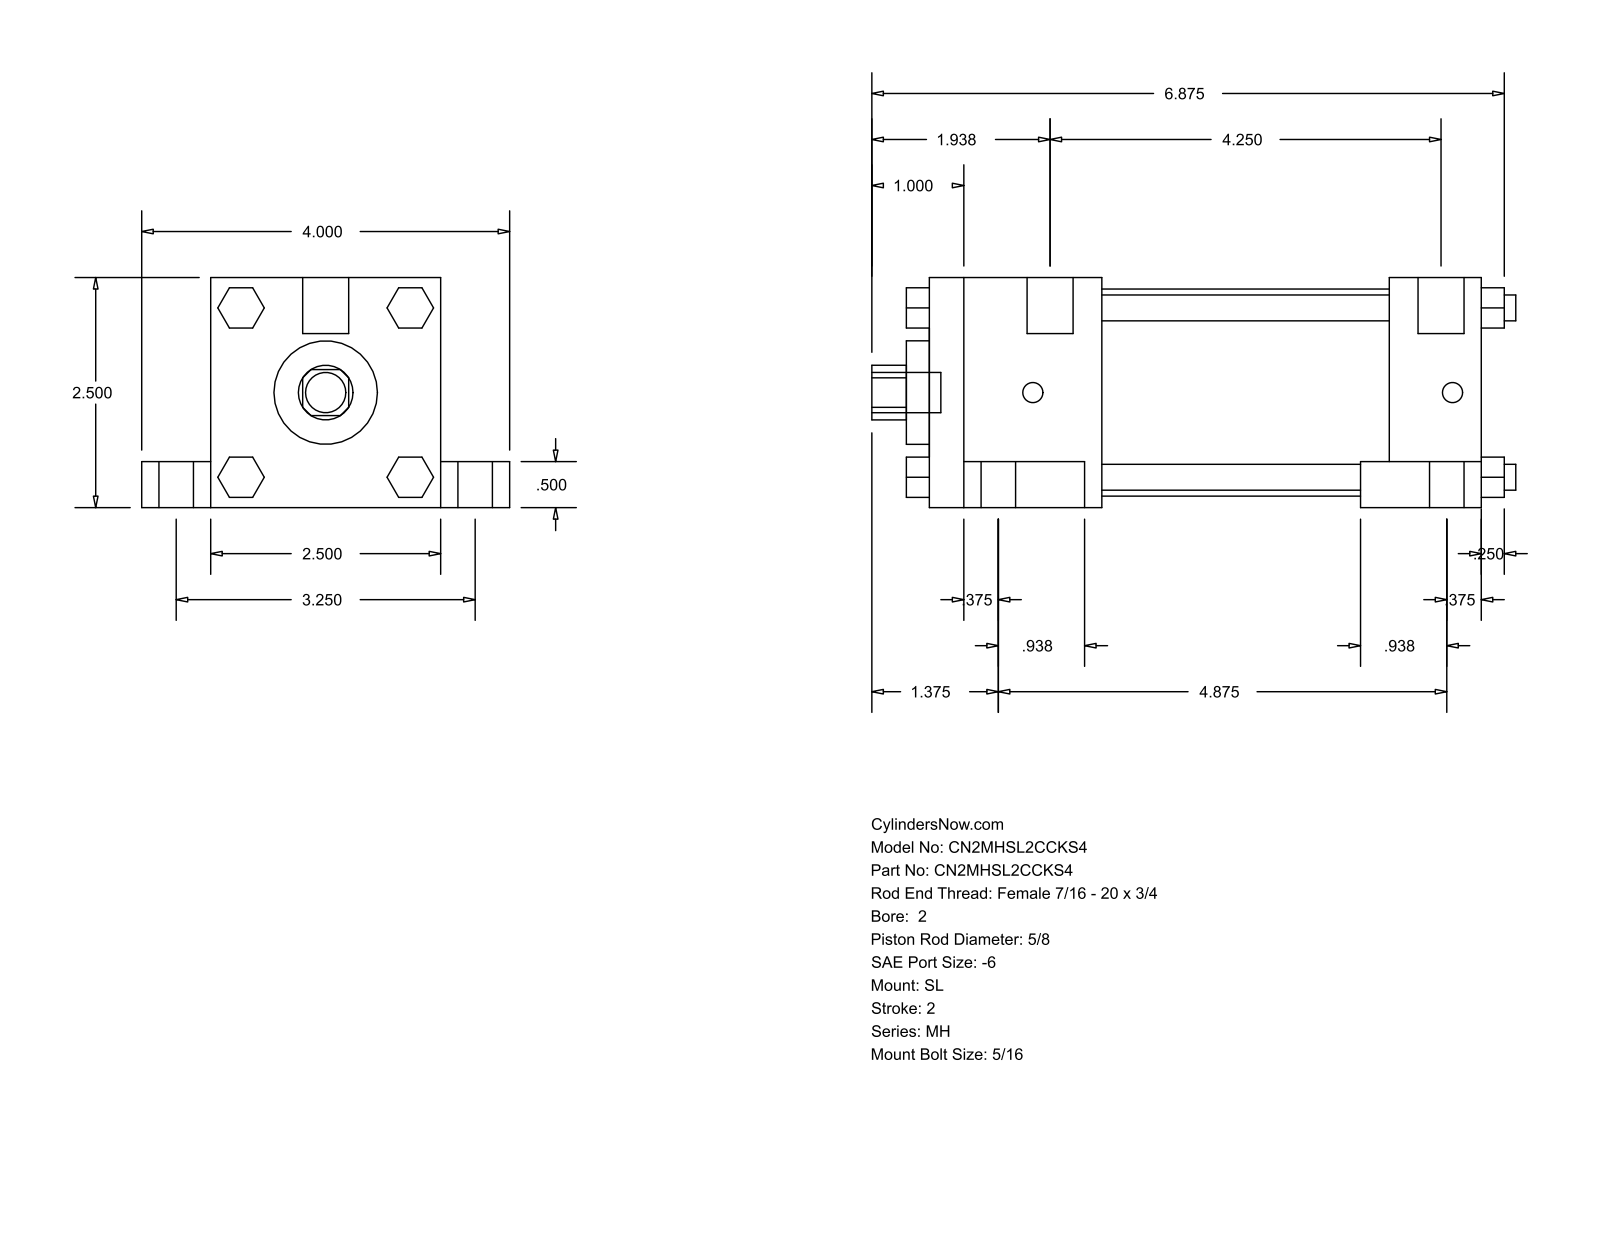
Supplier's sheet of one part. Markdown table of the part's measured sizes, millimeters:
| quantity | value |
| --- | --- |
| part name | MH_SL__0200_0.625 |
| STEP written by | GSSL Pune (CONFIG_CONTROL_DESIGN) |
| units | millimeters |
| bodies | 0 solids, 148 faces (112 planar, 36 cylindrical, 0 other) |
| overall size | 177.8 × 101.6 × 63.5 |
| round holes (diameter × count) | 15.88 × 1, 28.57 × 1, 57.15 × 1 |
| round bosses / shafts (diameter × count) | 15.88 × 4, 9.53 × 4, 7.14 × 4, 5.56 × 4, 12.7 × 2, 11.11 × 1 |
| partial cylindrical surfaces (radius × count) | 7.54 × 1 |
| main face-to-face distances | 63.5, 152.4, 12.7, 19.05, 50.8, 82.55, 25.4, 127, 47.62, 79.38 |
